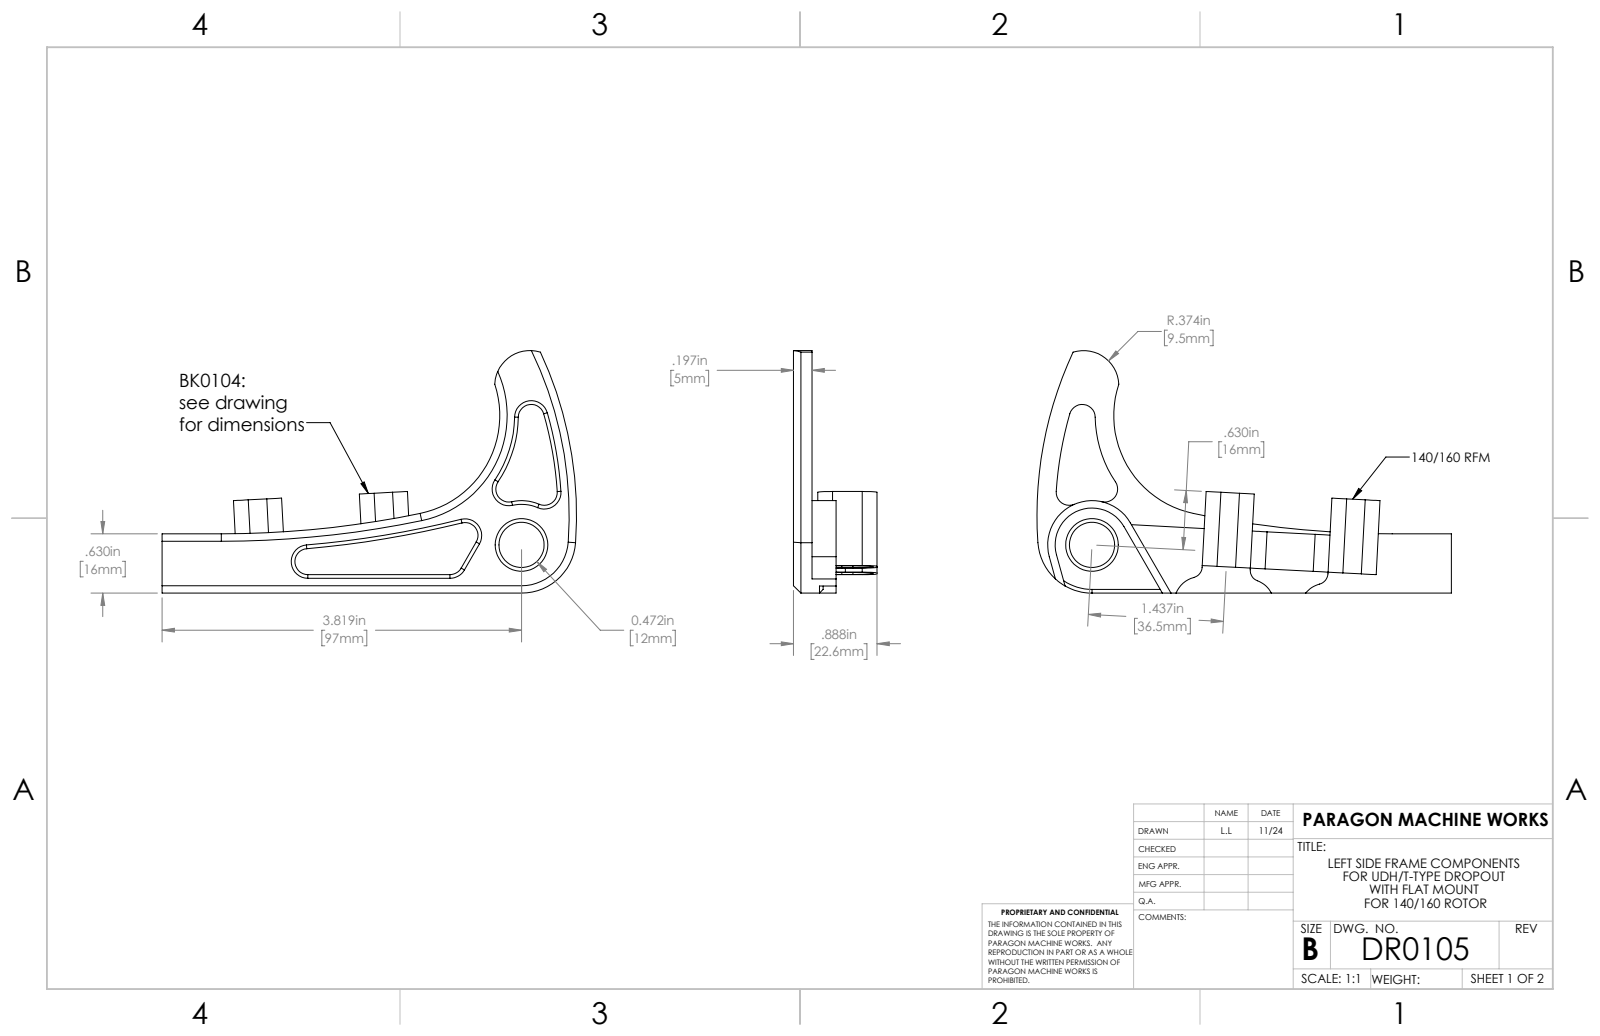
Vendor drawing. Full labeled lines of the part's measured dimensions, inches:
Part name (STEP PRODUCT): DR0102L
STEP written by: SolidWorks 2023 (AUTOMOTIVE_DESIGN)
Units: inches
Bodies: 1 solid, 77 faces (26 planar, 29 cylindrical, 22 other)
Overall size (bounding box): 4.404 × 2.575 × 0.453
Volume: 0.852 in³ · Surface area: 12.48 in²
Round holes (diameter × count): ⌀0.48 ×1
Partial cylindrical surfaces — rounded edges, fillets, slot ends (radius × count): R0.138 ×6, R0.118 ×3, R0.276 ×3, R0.374 ×1, R0.392 ×1, R0.47 ×1, R0.576 ×1, R1.061 ×1
Main face-to-face distances: 0.197, 0.118, 0.315, 0.079, 0.236, 0.453, 0.374, 0.256, 0.138, 0.394
